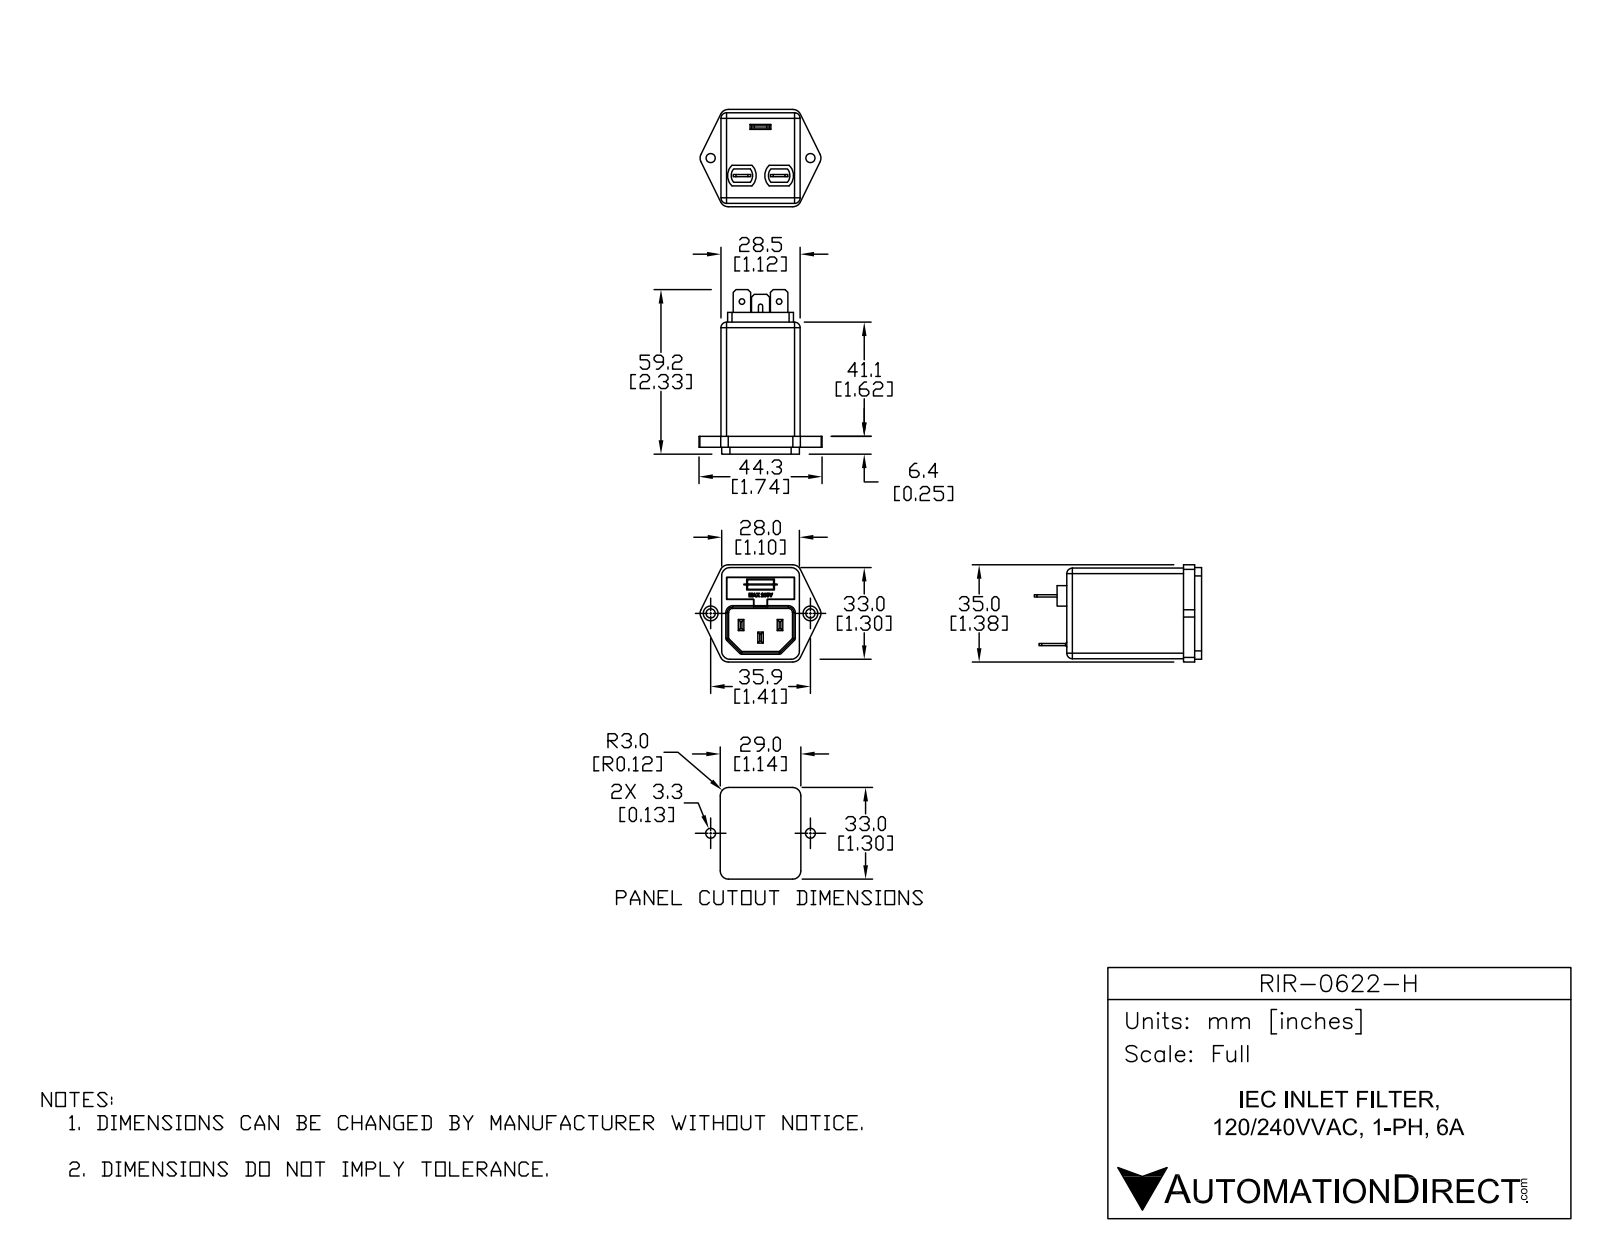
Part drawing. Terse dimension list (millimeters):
name: RIR0622H
written by: SolidWorks 2015 (AUTOMOTIVE_DESIGN)
unit: mm
bodies: 1 solid, 316 faces (209 planar, 56 cylindrical, 51 other)
size: 60.2 × 43.86 × 35
volume: 40 598 mm³; area: 10 976 mm²
holes: 2× ⌀2, 2× ⌀3.3
rounds: 20× R0.5, 10× R2, 2× R0.75, 2× R3.85, 2× R5.15, 1× R3
face distances: 28.5, 32.6, 14, 16.5, 48.5, 2, 4, 6.5, 26.25, 32
hole spacings: 13.4, 35.9
